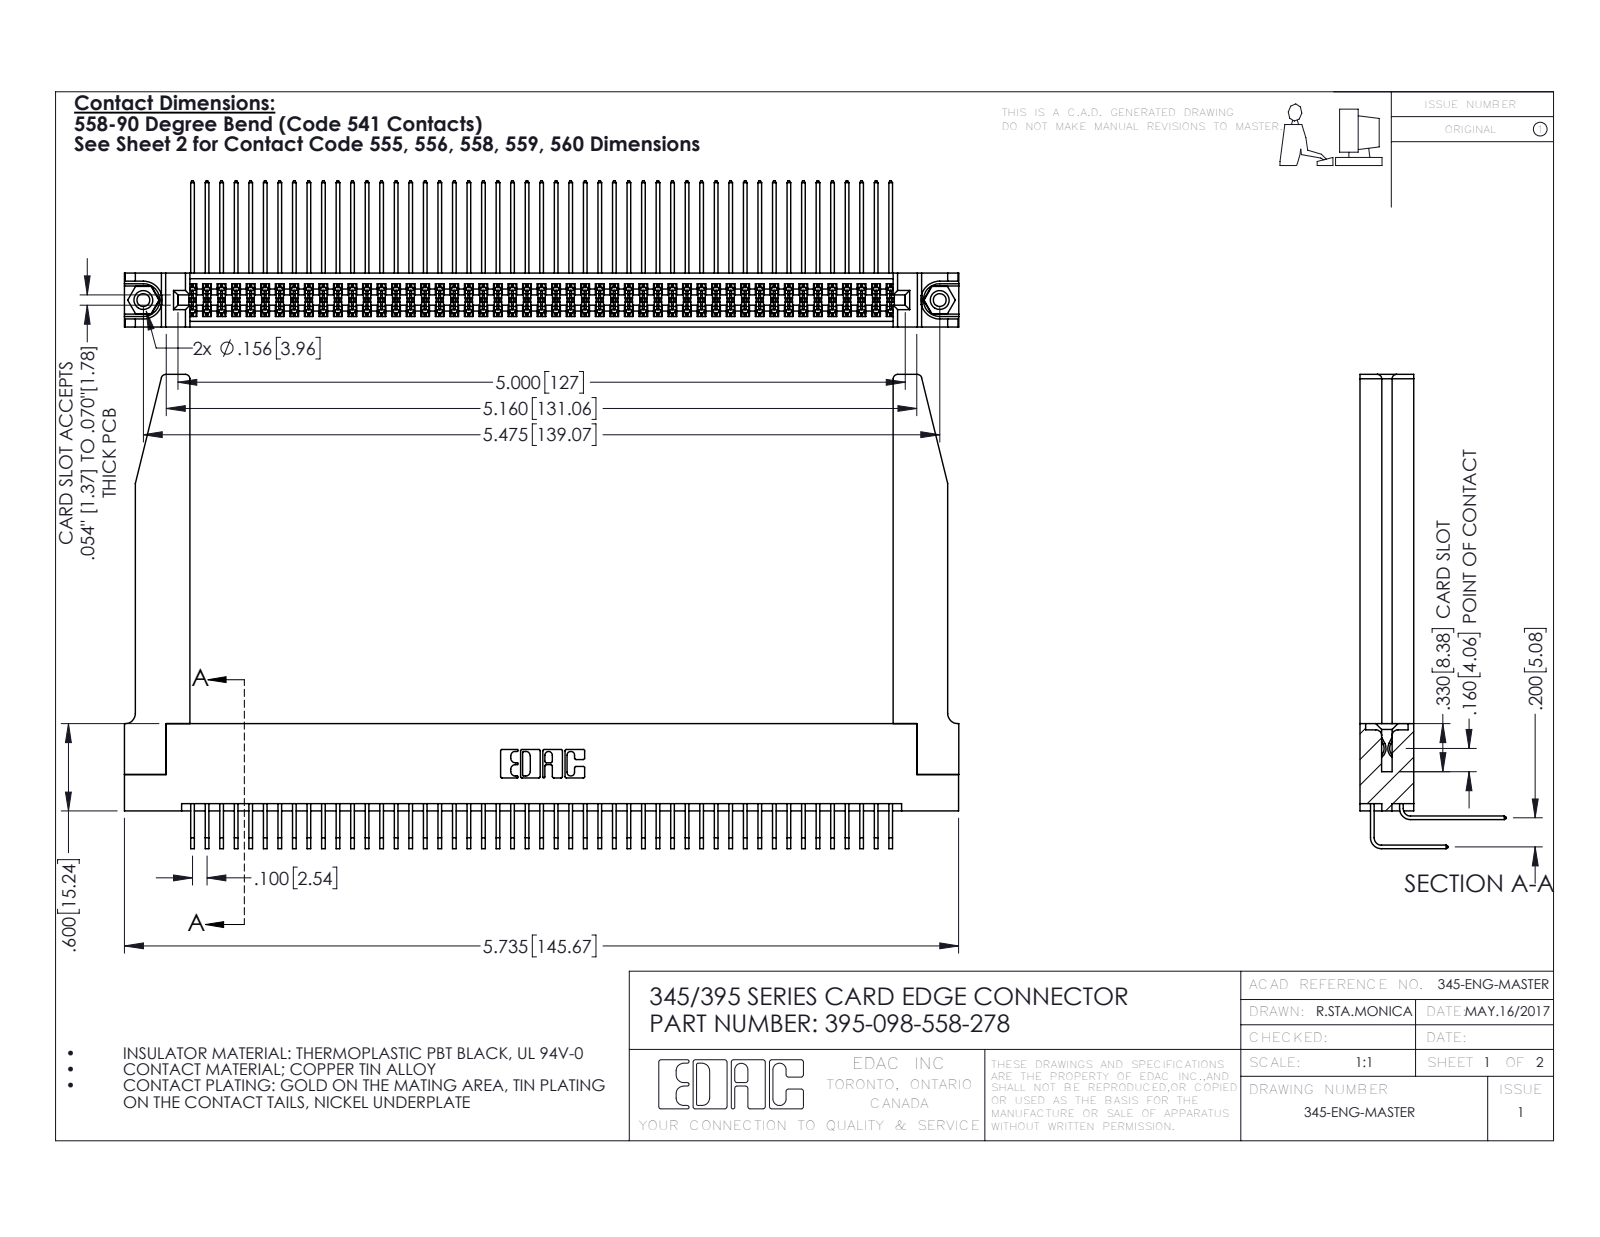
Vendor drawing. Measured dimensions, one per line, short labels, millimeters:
name: 345-292-001_558 559 Tail - 1; 345-250-001_345-250-001-102; 395-098-558-278; 345 Part_Flush Mounting Lugs - 0.156 Dia-TH (+2 more)
written by: SolidWorks 2016 (CONFIG_CONTROL_DESIGN)
unit: mm
bodies: 103 solids, 5456 faces (3652 planar, 1752 cylindrical, 52 other)
size: 145.7 × 82.8 × 25.5
volume: 22 550 mm³; area: 31 480 mm²
holes: 2× ⌀2.3, 2× ⌀3.2, 2× ⌀4, 1× ⌀1.6
bosses: 2× ⌀3.9
rounds: 148× R0.2, 22× R0.3, 8× R0.8, 6× R0.2, 6× R0.8, 3× R0.7, 2× R0.4, 2× R0.5
face distances: 1.8, 9.4, 7.6, 5.1, 2.5, 6.9, 0.6, 5.7, 7.2, 0.6
hole spacings: 6.9, 133.1, 139.1
